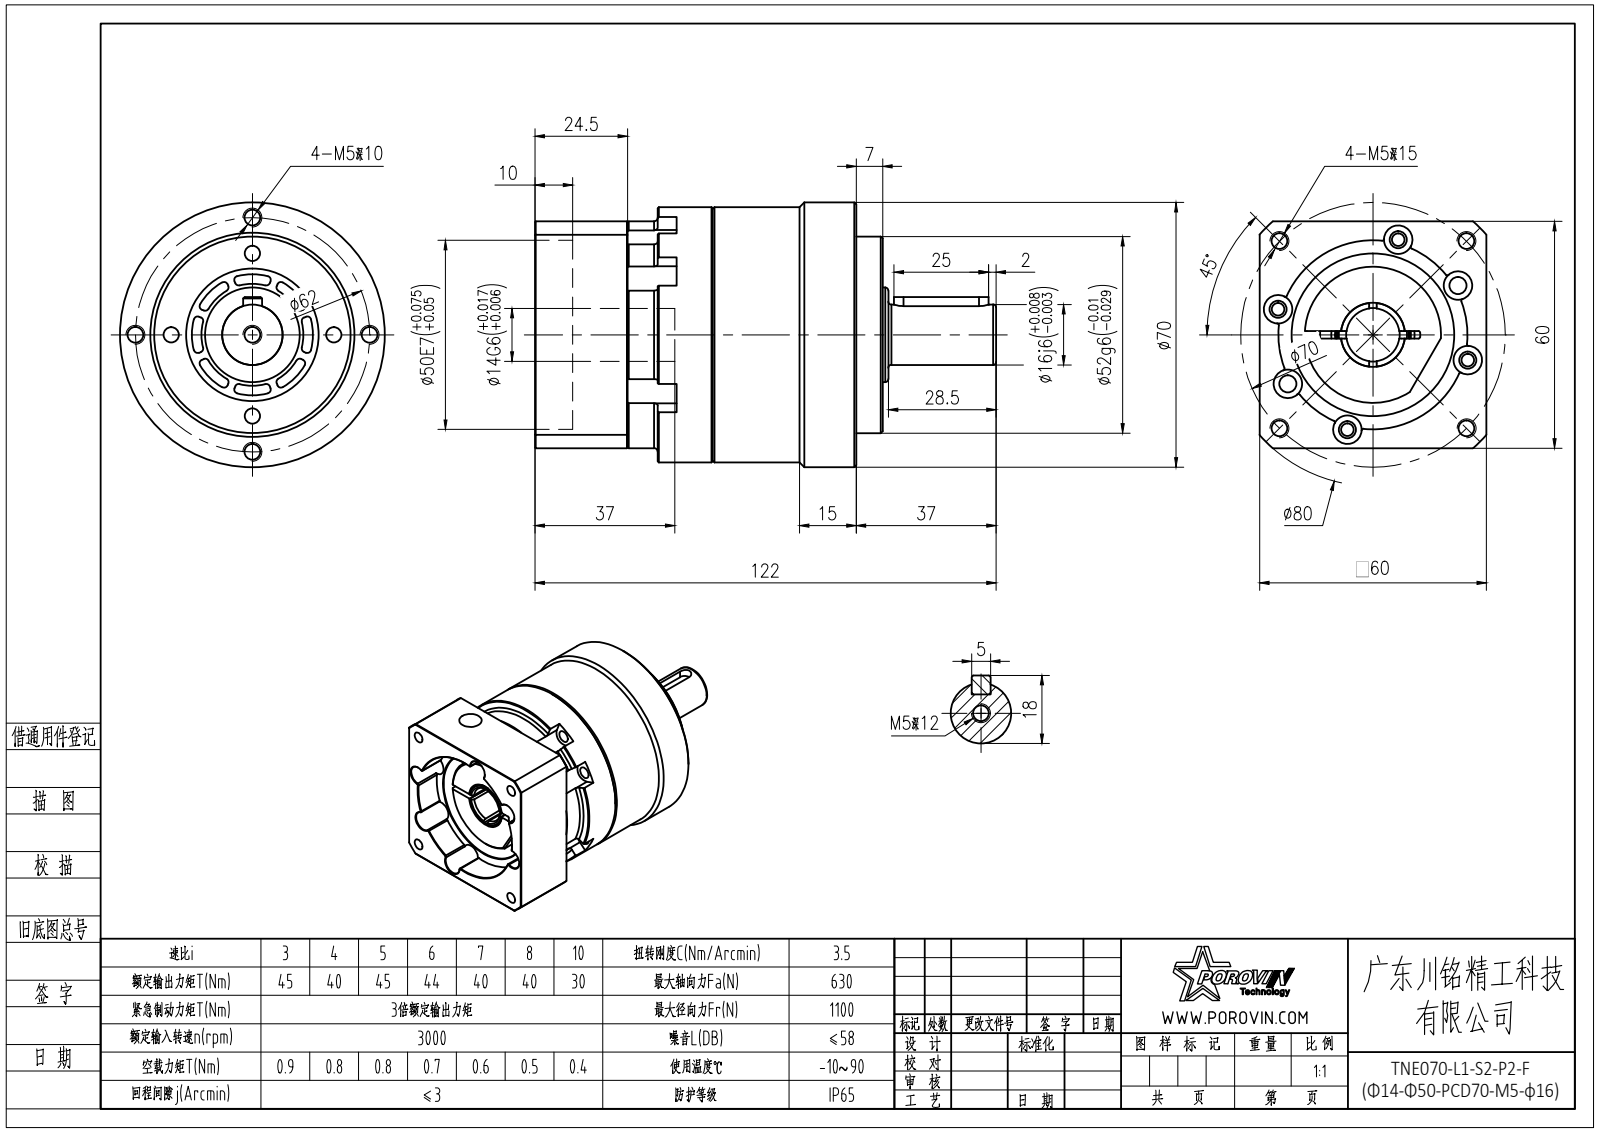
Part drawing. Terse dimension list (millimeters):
name: 一级齿圈加出轴 KE70外形图; hexagon socket head cap screws gb_GB_FASTENER_SCREWS_HSHCS M4X16-N; spring lock washers--normal type gb_GB_FASTENER_WASHER_SW 4; hexagon socket head cap screws gb_GB_FASTENER_SCREWS_HSHCS M4X20-N (+2 more)
written by: SolidWorks 2016 (CONFIG_CONTROL_DESIGN)
unit: mm
bodies: 32 solids, 1045 faces (387 planar, 392 cylindrical, 266 other)
size: 122 × 70 × 70
volume: 257 136 mm³; area: 66 484 mm²
holes: 12× ⌀4.4, 12× ⌀4.5, 10× ⌀4.2, 6× ⌀3.3, 6× ⌀7.5, 4× ⌀4, 2× ⌀5.5, 1× ⌀8.5, 1× ⌀14, 1× ⌀14.2, 1× ⌀25, 1× ⌀35
bosses: 12× ⌀7, 12× ⌀6.6, 12× ⌀4, 1× ⌀70, 1× ⌀67.5, 1× ⌀52, 1× ⌀36, 1× ⌀22.5
rounds: 36× R0.5, 32× R1, 6× R3.75, 2× R2.5, 1× R4.75, 1× R13.5, 1× R16, 1× R30
face distances: 5, 22.5, 60, 38, 11, 27.5, 29, 2, 33, 60.5
hole spacings: 61, 24.96, 25.53, 37.73, 52.46, 8.62, 26, 30.5
